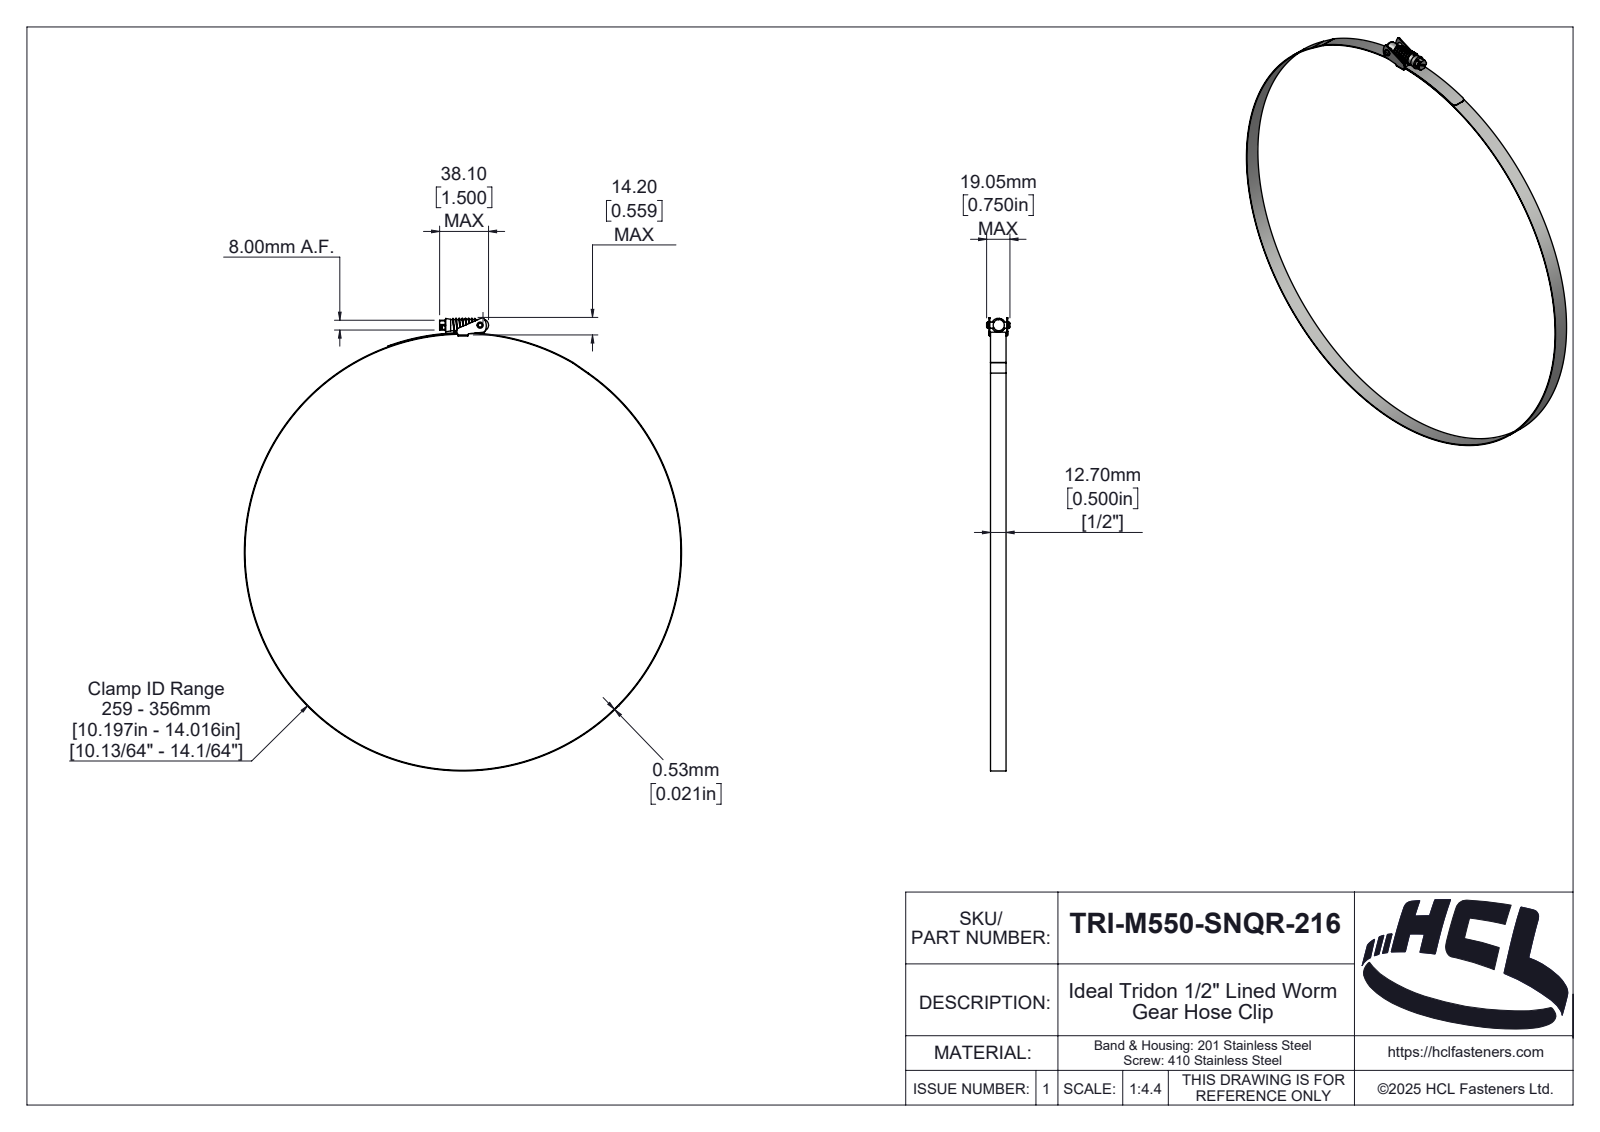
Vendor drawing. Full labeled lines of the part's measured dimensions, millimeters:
Part name (STEP PRODUCT): TRI-M550-SNQR-216
STEP written by: SolidWorks 2025 (AUTOMOTIVE_DESIGN)
Units: millimetres
Bodies: 5 solids, 222 faces (44 planar, 112 cylindrical, 66 other)
Overall size (bounding box): 370.02 × 357.06 × 19.05
Volume: 11 140 mm³ · Surface area: 34 881 mm²
Round holes (diameter × count): ⌀5 ×1, ⌀356 ×1
Round bosses / shafts (diameter × count): ⌀357.06 ×1, ⌀9.1 ×1
Partial cylindrical surfaces — rounded edges, fillets, slot ends (radius × count): R1 ×11, R0.1 ×2, R0.9 ×2, R3 ×2, R0.46 ×1, R1.89 ×1, R2 ×1, R2.35 ×1
Main face-to-face distances: 12.7, 0.8, 1.35, 14.05, 14.6, 0.55, 13.25, 15.4, 0.53, 13.8
Hole centre spacings: 185.93
